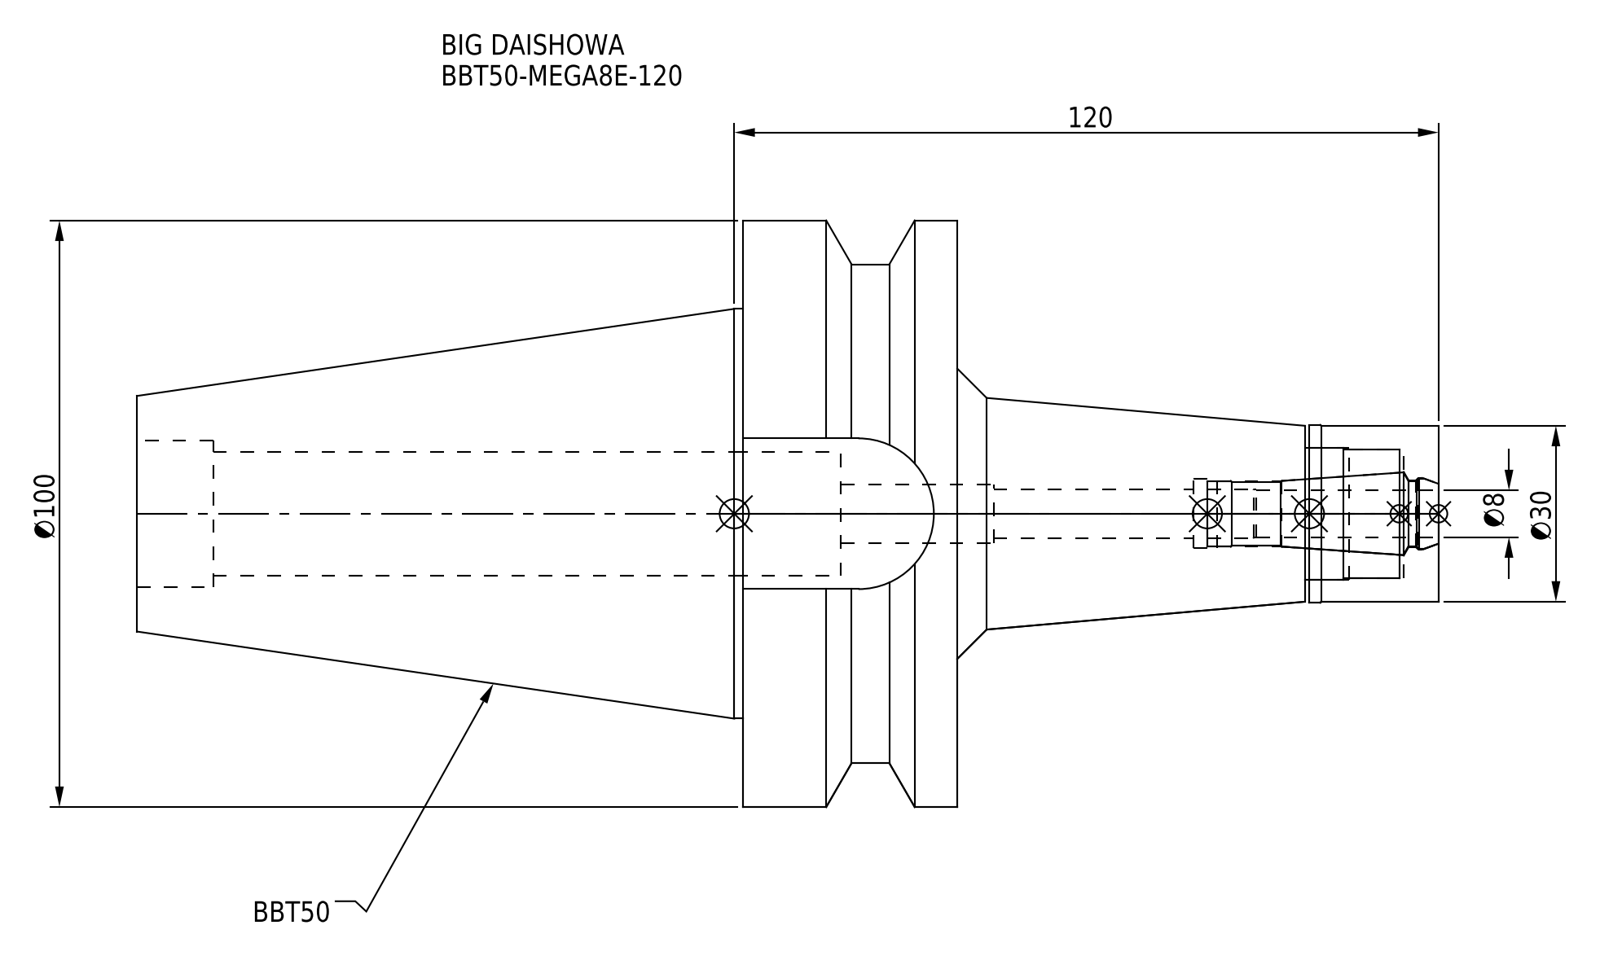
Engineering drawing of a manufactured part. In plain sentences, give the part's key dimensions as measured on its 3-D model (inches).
The part is named "BBT50-MEGA8E-120-080-FreeParts; BBT50-MEGA8E-120_1.stp; BBT50-MEGA8E-120-080.stp; BBT50-MEGA8E-120 (+3 more)". Its 3-D file was written by "SolidWorks 2019 (CONFIG_CONTROL_DESIGN)". It is 2 solids with 81 faces: 21 planar, 40 cylindrical and 20 other. Overall it measures 8.732 by 3.937 by 3.937 inches. Its volume is 31.81 cubic inches and its surface area 105.2 square inches. Round holes: 1 of diameter 0.331, 1 of diameter 0.394, 1 of diameter 0.441, 1 of diameter 0.449, 1 of diameter 0.465, 1 of diameter 0.484, 1 of diameter 0.835, 1 of diameter 0.866, 1 of diameter 0.886, 1 of diameter 0.984. Round bosses or shafts: 1 of diameter 3.937, 1 of diameter 3.346, 1 of diameter 2.75, 1 of diameter 1.193, 1 of diameter 1.181. Partial cylindrical surfaces (rounded edges, fillets, slot ends): 1 of radius 0.506. The main face-to-face distances are 1.437, 4.067, 5.504, 2.787, 3.228, 4.665, 8.732, 1.012, 0.866, 2.362.
